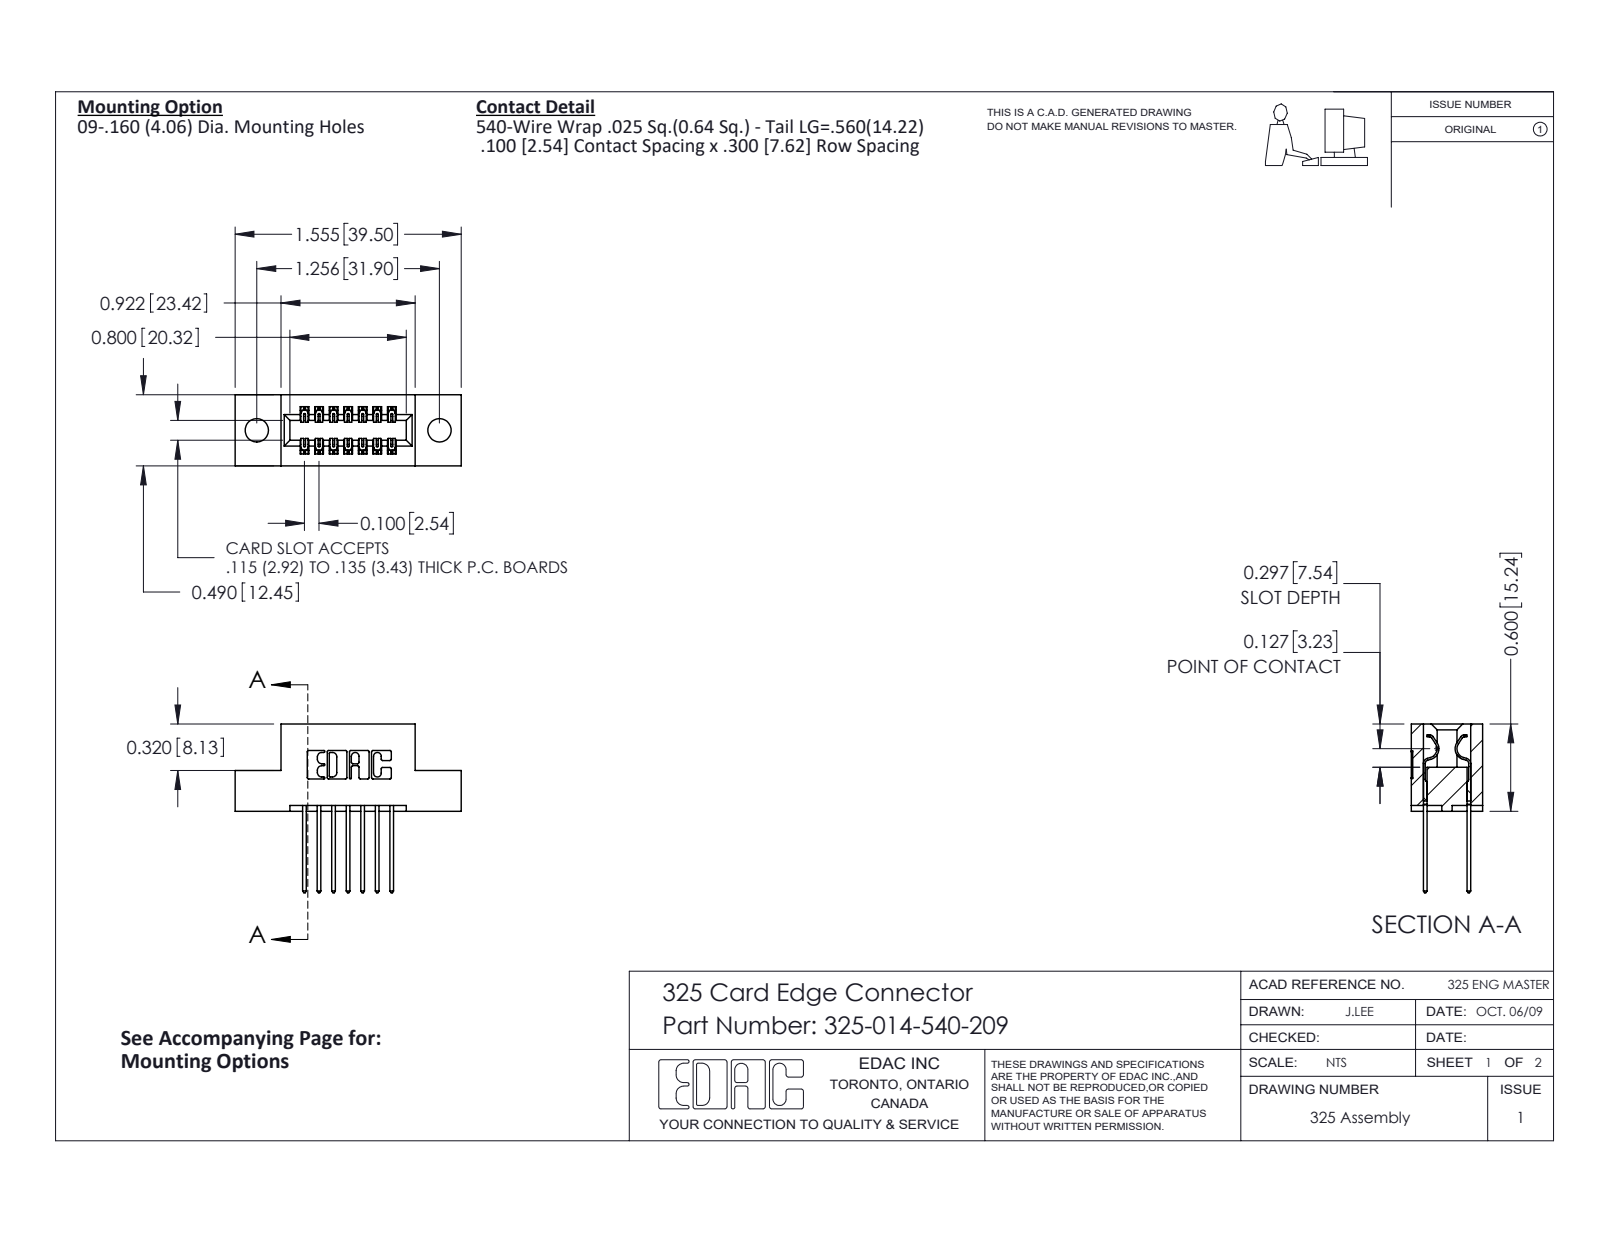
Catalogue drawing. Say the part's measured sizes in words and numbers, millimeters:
The part is named "325-014-540-209; 325 Part_.160 TH; 325-292-001_325-293-140". Its 3-D file was written by "SolidWorks 2016 (CONFIG_CONTROL_DESIGN)". It is 15 solids with 842 faces: 574 planar, 268 cylindrical and 0 other. Overall it measures 39.5 by 29.5 by 12.4 millimeters. Its volume is 4 600 cubic millimeters and its surface area 4 919 square millimeters. Round holes: 2 of diameter 4.1. Partial cylindrical surfaces (rounded edges, fillets, slot ends): 22 of radius 0.3, 21 of radius 0.2, 14 of radius 0.3, 6 of radius 0.2, 6 of radius 0.8, 3 of radius 0.7, 2 of radius 0.4, 2 of radius 0.6. The main face-to-face distances are 7.6, 2.1, 10.3, 2.5, 1, 5.1, 12.4, 2.7, 9.7, 0.6. The hole center spacings are 31.9.
